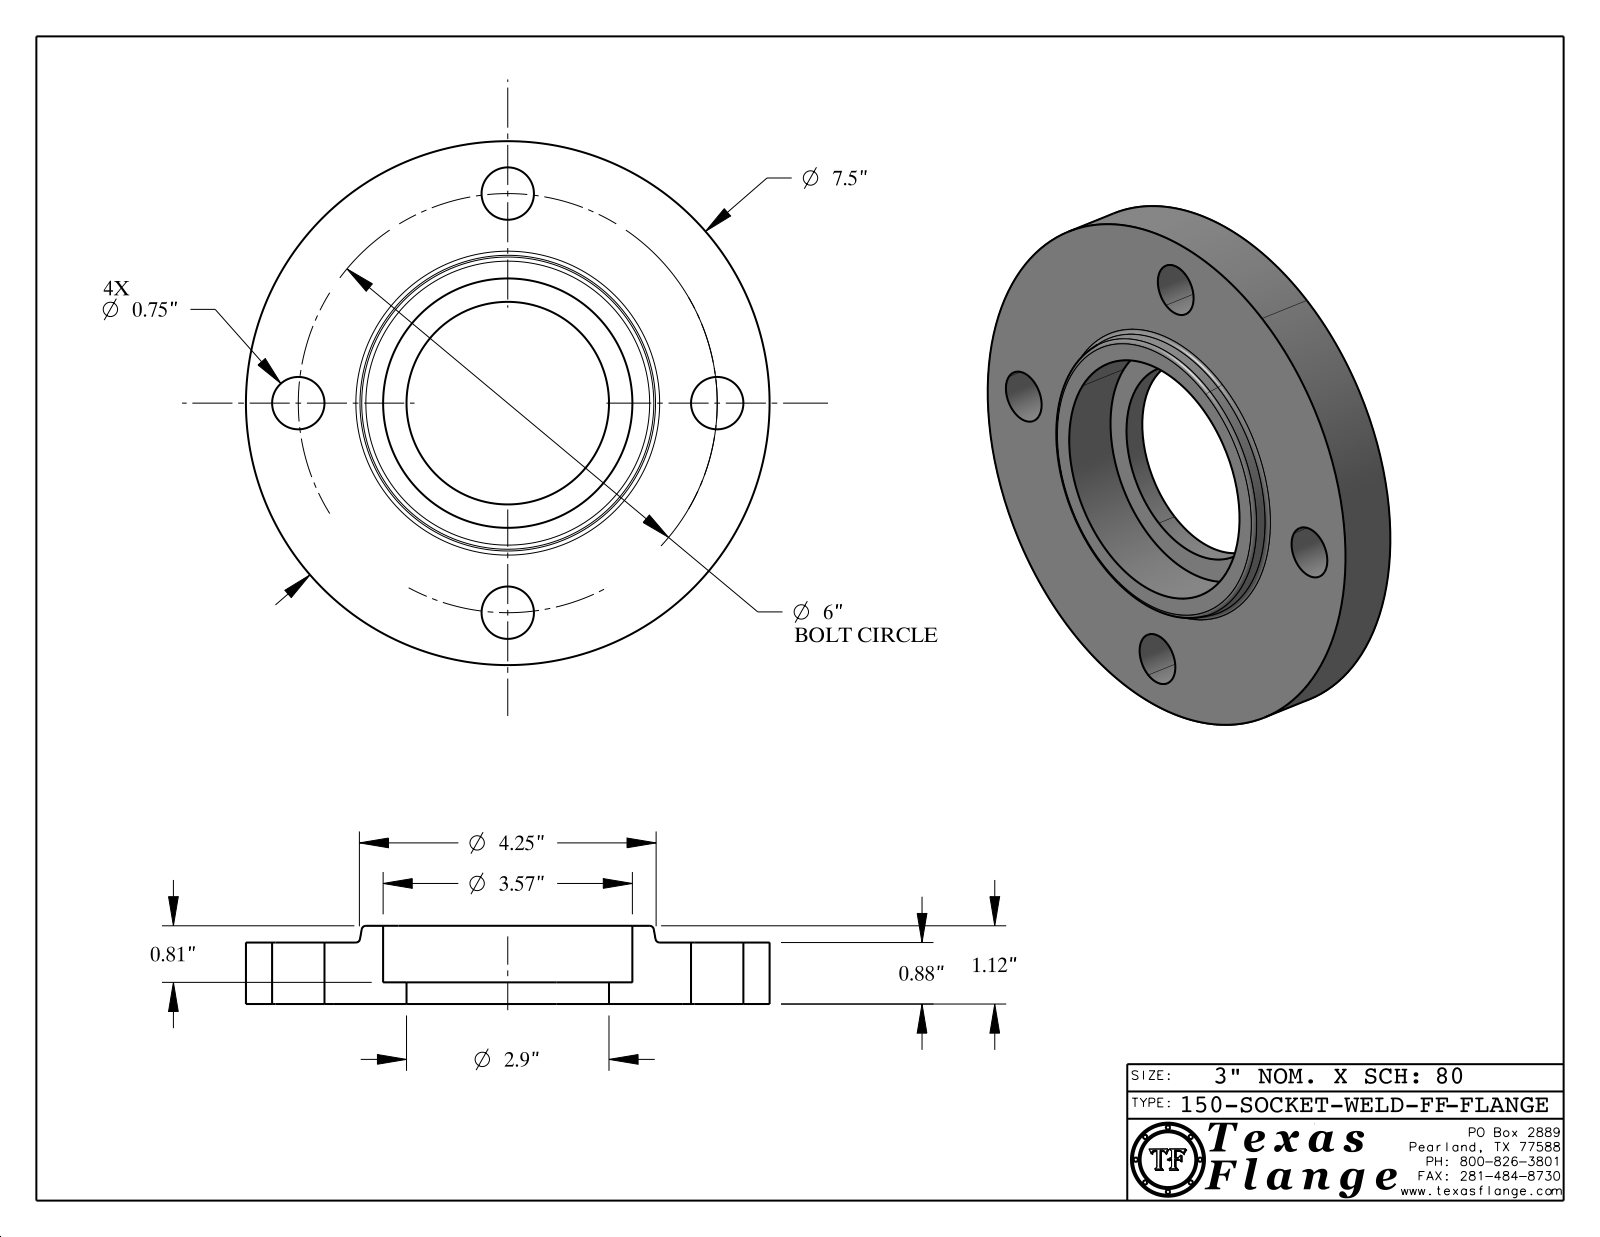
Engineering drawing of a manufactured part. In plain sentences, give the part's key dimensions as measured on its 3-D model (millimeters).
The part is named "150-SOCKET-WELD-FF". Its 3-D file was written by "CATIA V5 STEP AP214 (AUTOMOTIVE_DESIGN)". It is 1 solid with 410 faces: 370 planar, 34 cylindrical and 6 other. Overall it measures 190.5 by 190.5 by 28.4 millimeters. Its volume is 499 800 cubic millimeters and its surface area 74 130 square millimeters. Round holes: 4 of diameter 19.1, 1 of diameter 12.6, 1 of diameter 73.7, 1 of diameter 90.7. Round bosses or shafts: 8 of diameter 0.8, 1 of diameter 190.5, 1 of diameter 9.9. The main face-to-face distances are 22.4, 7.9, 14.5, 28.4, 20.6, 6.1, 22, 14.1, 0.4, 6.5. The hole center spacings are 76.2, 107.8, 58.3, 140.8, 152.4.
